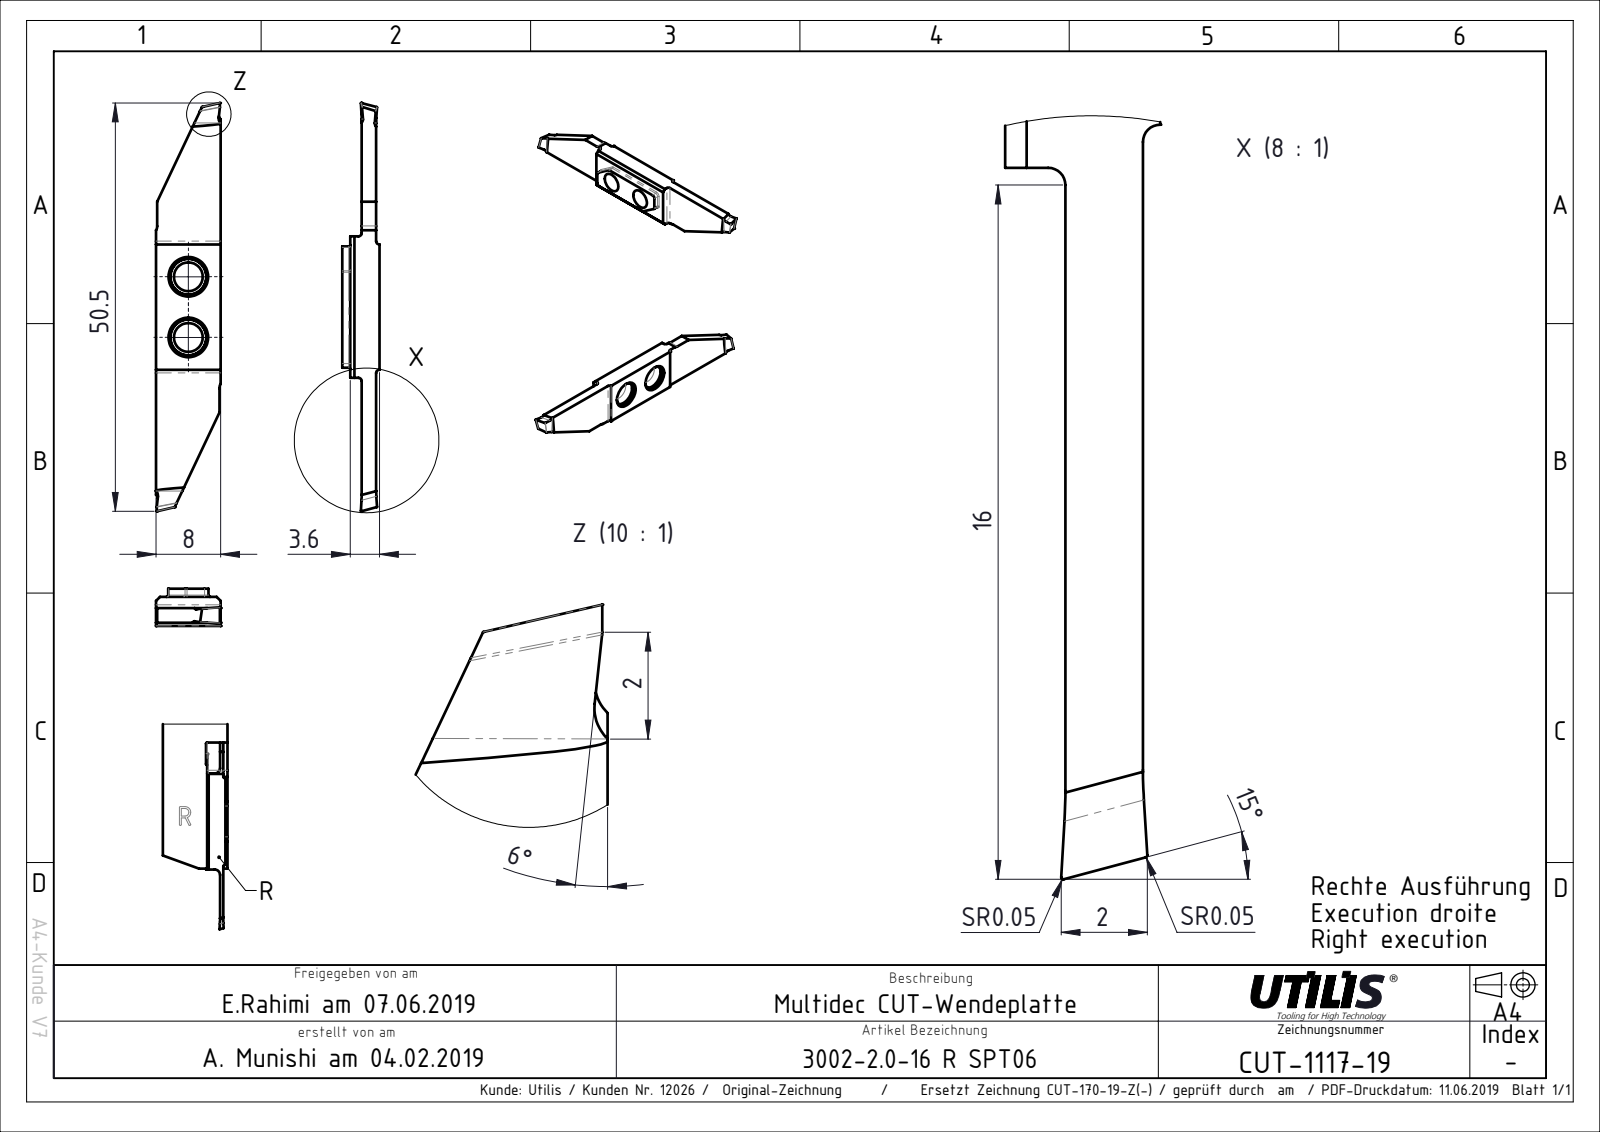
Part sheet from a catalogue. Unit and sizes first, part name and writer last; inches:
Units: inches
Overall size (bounding box): 1.988 × 0.315 × 0.142
Round holes (diameter × count): ⌀0.14 ×2
Partial cylindrical surfaces — rounded edges, fillets, slot ends (radius × count): R0.016 ×4, R0.039 ×2
Main face-to-face distances: 0.071, 0.087, 0.016, 0.055, 0.126, 0.142, 0.315, 0.712, 0.309, 0.689
Hole centre spacings: 0.295
Volume: 0.046 in³ · Surface area: 1.49 in²
Bodies: 1 solid, 40 faces (24 planar, 16 cylindrical, 0 other)
Part name (STEP PRODUCT): CUT-1117; ASME Y14.5
STEP written by: FormatWorks Professional (AP242_MANAGED_MODEL_BASED_3D_ENGINEERING_MIM_LF)
